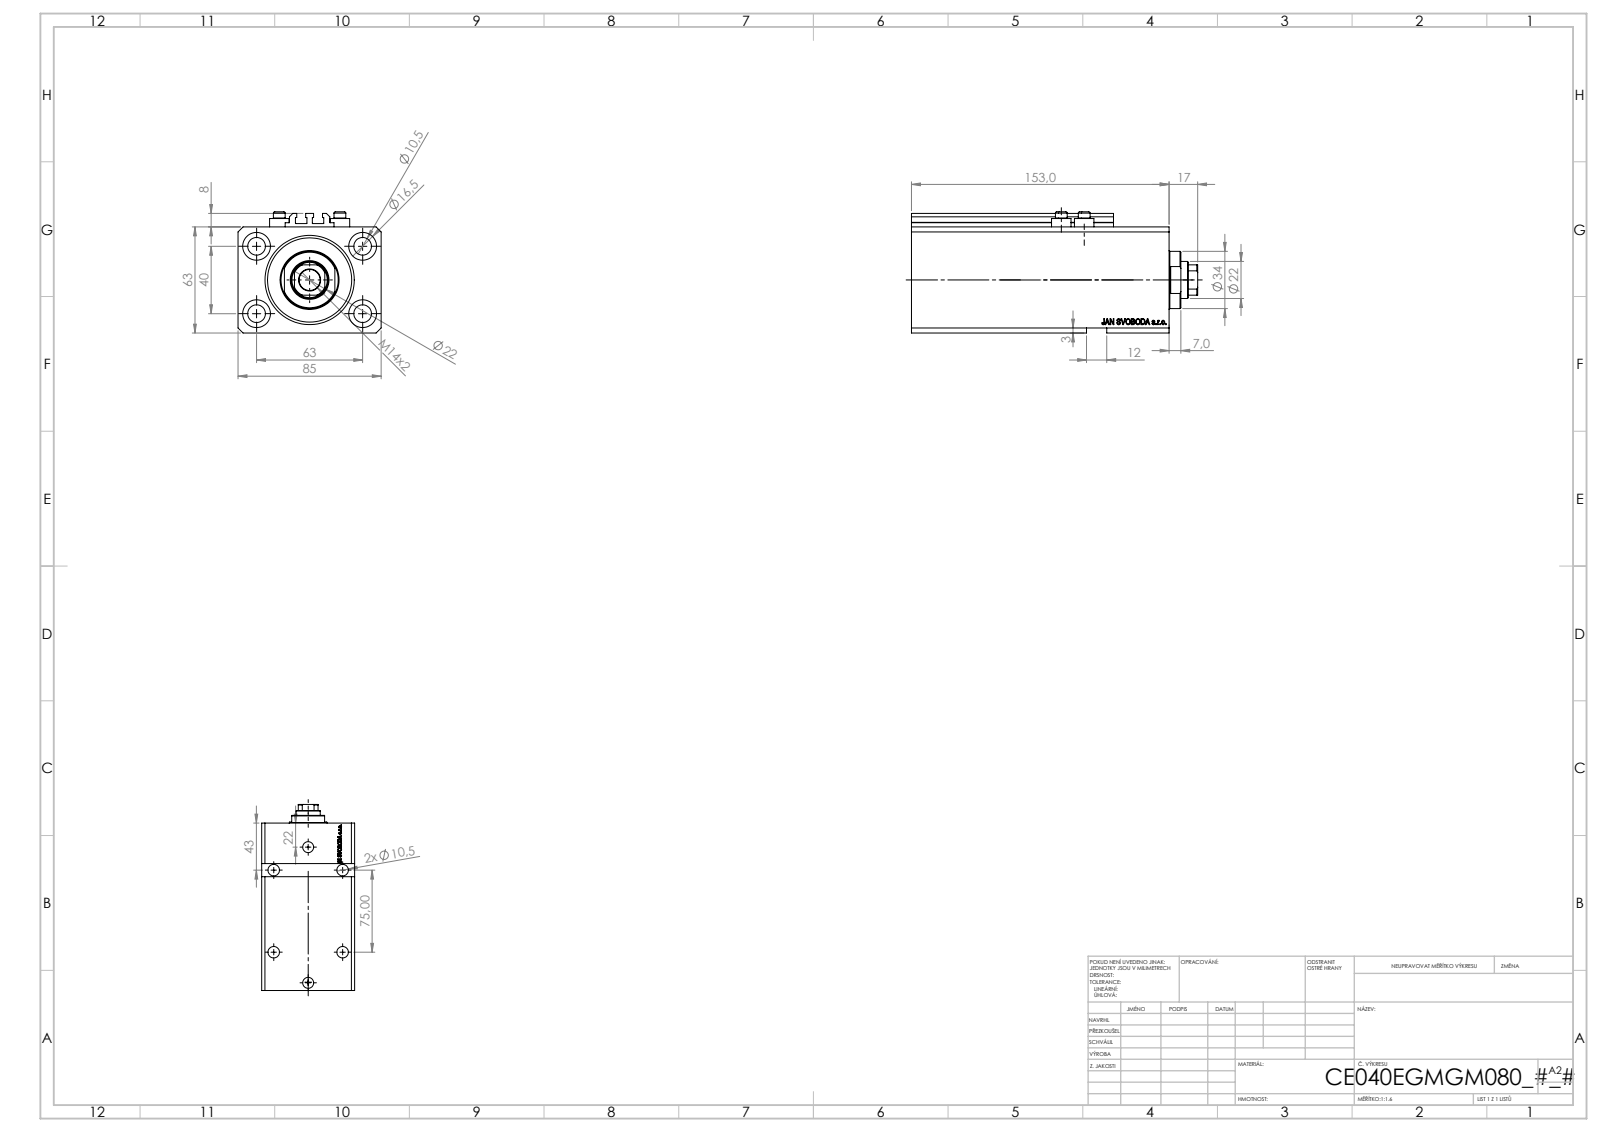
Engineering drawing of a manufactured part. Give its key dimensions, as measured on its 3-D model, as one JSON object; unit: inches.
{"part_name": "ALLEN BOLT V250CE; V250CE_E_Body; V250CE_C_VCP; V250CE_VC_E", "step_written_by": "SolidWorks 2019 (CONFIG_CONTROL_DESIGN)", "units": "inches", "bodies": {"solids": 8, "faces": 1107, "planar": 535, "cylindrical": 146, "other": 426}, "overall_size": [6.693, 3.346, 2.835], "volume_in3": 41.73, "surface_area_in2": 218.3, "round_holes": [[0.413, 8], [0.049, 4], [0.157, 4], [0.65, 4], [0.394, 2], [0.518, 2], [0.787, 2], [0.492, 1], [0.866, 1], [1.575, 1], [2.087, 1]], "round_bosses_or_shafts": [[0.457, 4], [0.276, 4], [1.339, 1]], "partial_cylinders_radius": [[0.008, 10], [0.413, 1]], "face_to_face_distances": [2.48, 3.346, 6.024, 0.669, 5.354, 0.449, 4.906, 5.575, 0.118, 2.559], "hole_center_spacings": [1.469, 2.48, 0.535, 0.606, 0.983, 1.324, 1.417, 1.491]}
